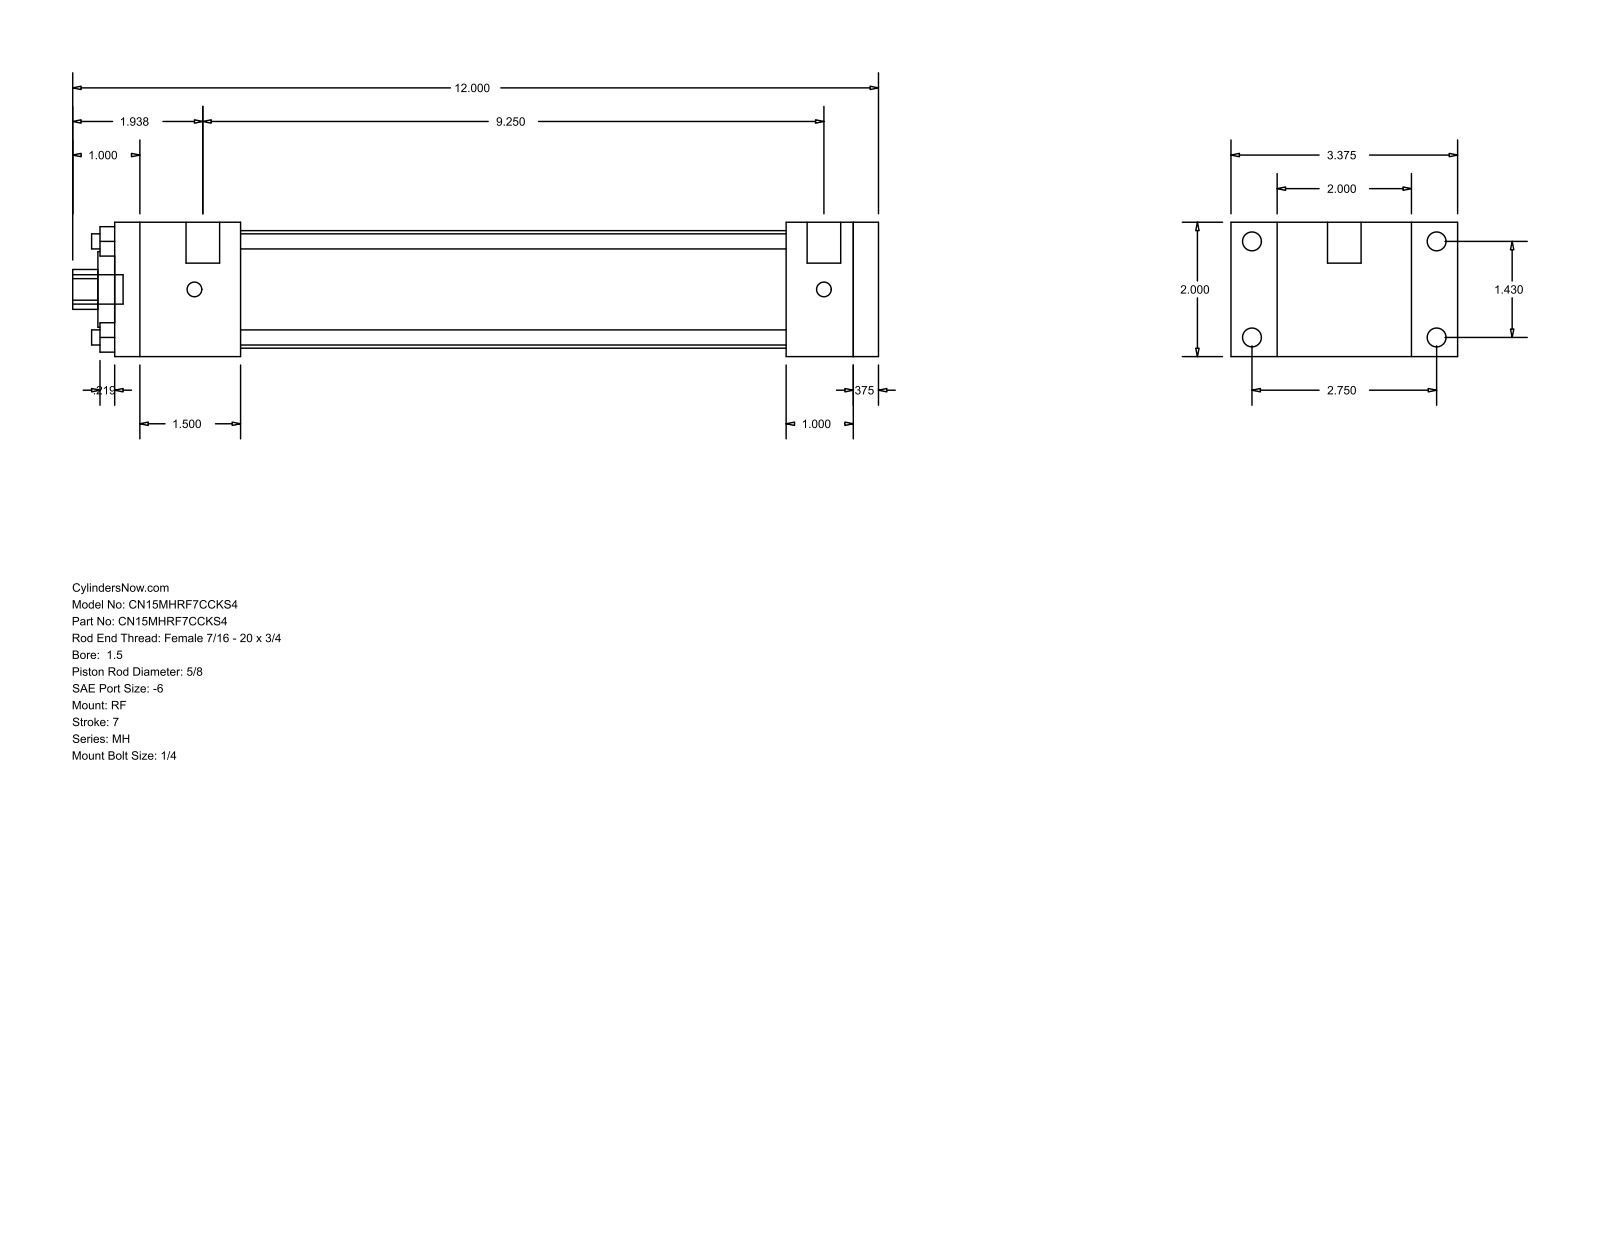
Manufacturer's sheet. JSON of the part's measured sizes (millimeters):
{"part_name": "MH_RF__0150_0.625", "step_written_by": "GSSL Pune (CONFIG_CONTROL_DESIGN)", "units": "millimeters", "bodies": {"solids": 0, "faces": 92, "planar": 64, "cylindrical": 28, "other": 0}, "overall_size": [304.8, 85.72, 50.8], "round_holes": [[5.71, 4], [15.88, 1], [28.57, 1], [44.45, 1]], "round_bosses_or_shafts": [[7.14, 4], [5.56, 4], [12.7, 2], [11.11, 1]], "partial_cylinders_radius": [[7.54, 1]], "face_to_face_distances": [50.8, 9.53, 288.92, 279.39, 17.46, 68.26, 254, 25.39, 34.92, 47.62], "hole_center_spacings": [25.68, 36.32, 51.36]}
